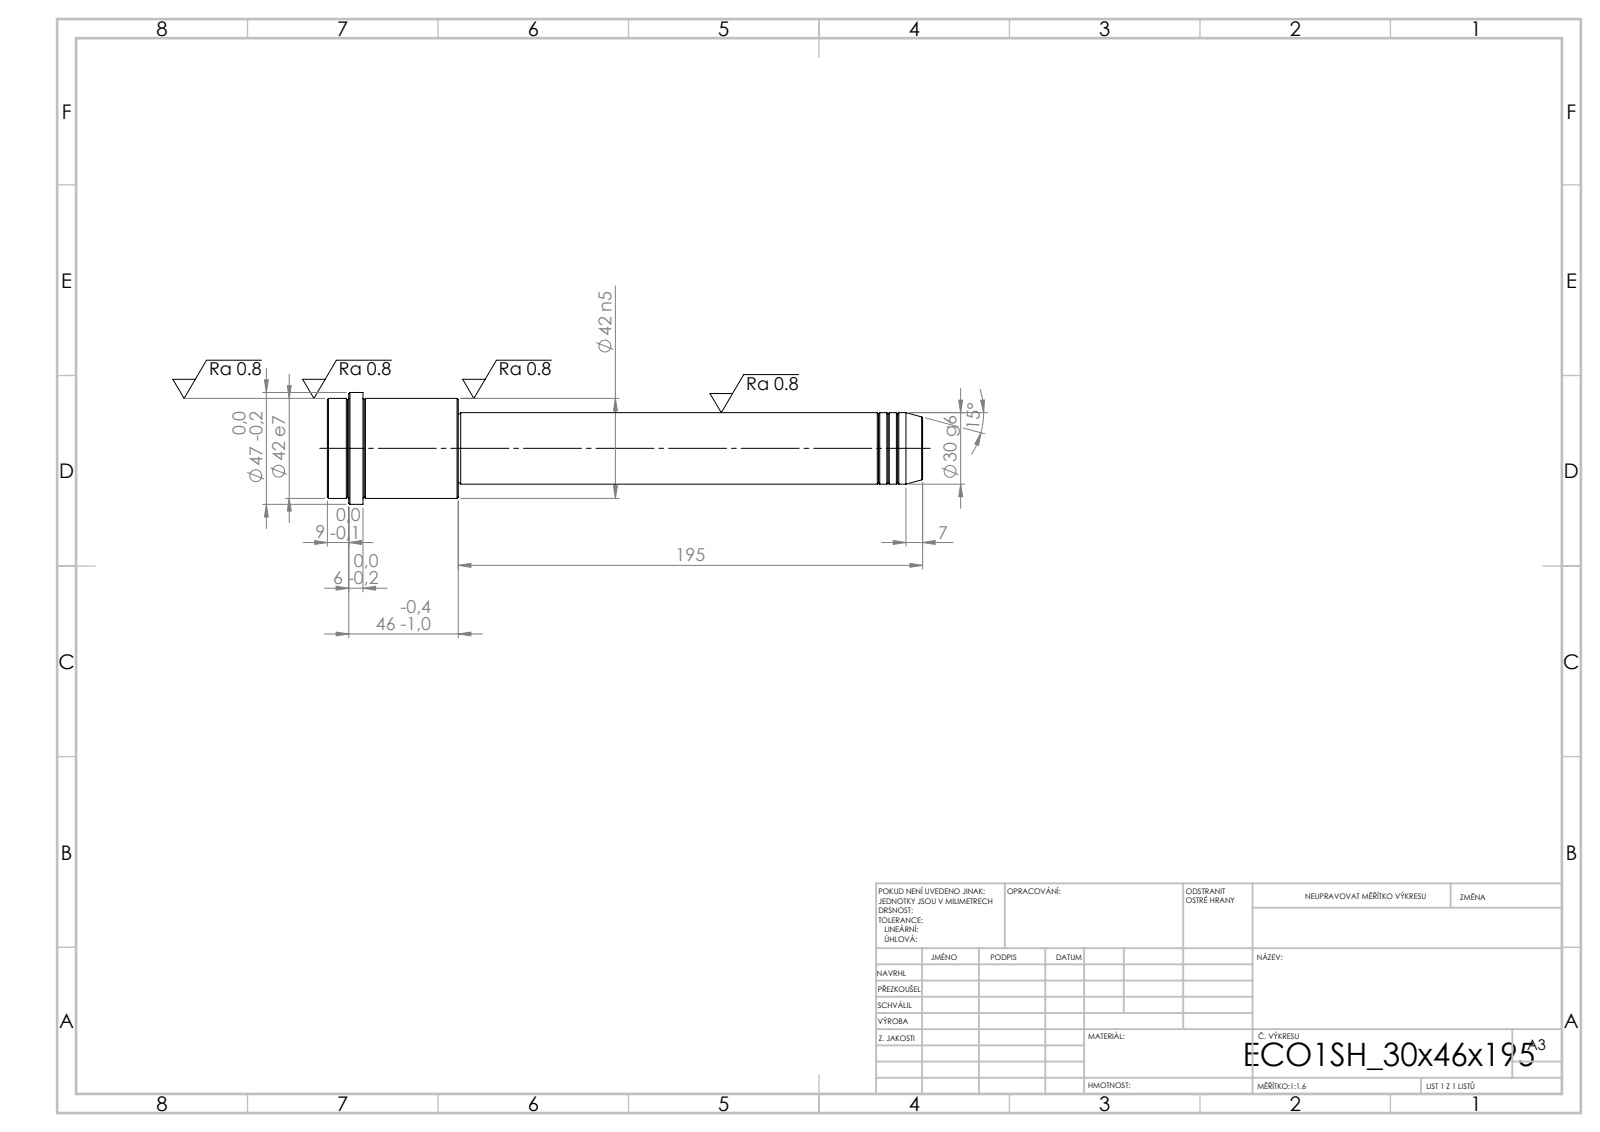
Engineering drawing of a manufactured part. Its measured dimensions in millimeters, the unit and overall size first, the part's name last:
Units: millimetres
Overall size (bounding box): 250 × 47 × 47
Round bosses / shafts (diameter × count): ⌀47 ×1, ⌀42 ×1, ⌀30 ×1, ⌀29 ×1
Main face-to-face distances: 55, 195, 250, 235, 40, 15, 241, 46, 6, 9
Volume: 215 229 mm³ · Surface area: 29 269 mm²
Bodies: 1 solid, 52 faces (6 planar, 16 cylindrical, 30 other)
STEP written by: SolidWorks 2019 (CONFIG_CONTROL_DESIGN)
